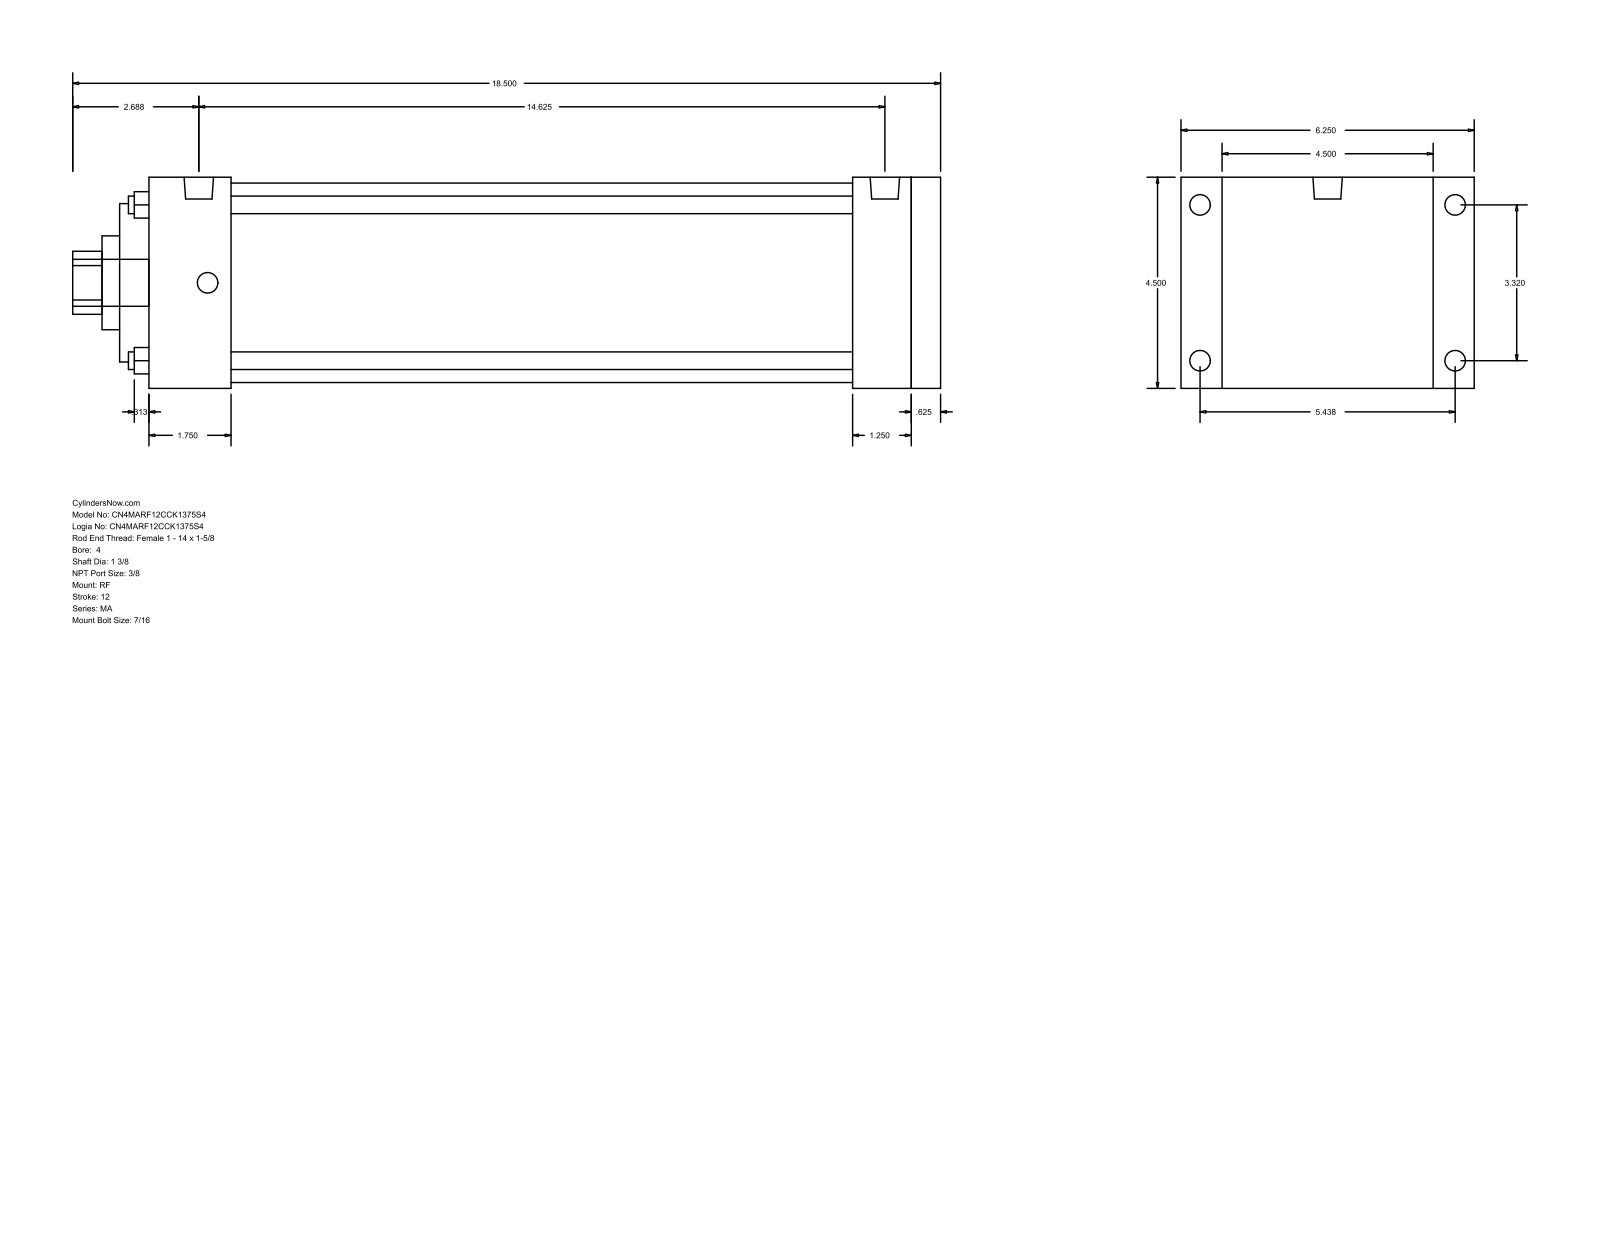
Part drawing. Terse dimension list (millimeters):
name: MA_RF__0400_1.375
written by: GSSL Pune (CONFIG_CONTROL_DESIGN)
unit: mm
bodies: 0 solids, 94 faces (65 planar, 29 cylindrical, 0 other)
size: 469.9 × 158.75 × 114.3
holes: 4× ⌀9.53, 1× ⌀34.92, 1× ⌀50.8, 1× ⌀85.72, 1× ⌀107.95
bosses: 8× ⌀11.11, 2× ⌀15.93, 1× ⌀25.4
rounds: 1× R17.06
face distances: 114.3, 428.63, 15.88, 412.75, 15.87, 428.62, 444.5, 22.23, 136.53, 396.87
hole spacings: 59.62, 84.32, 119.25
